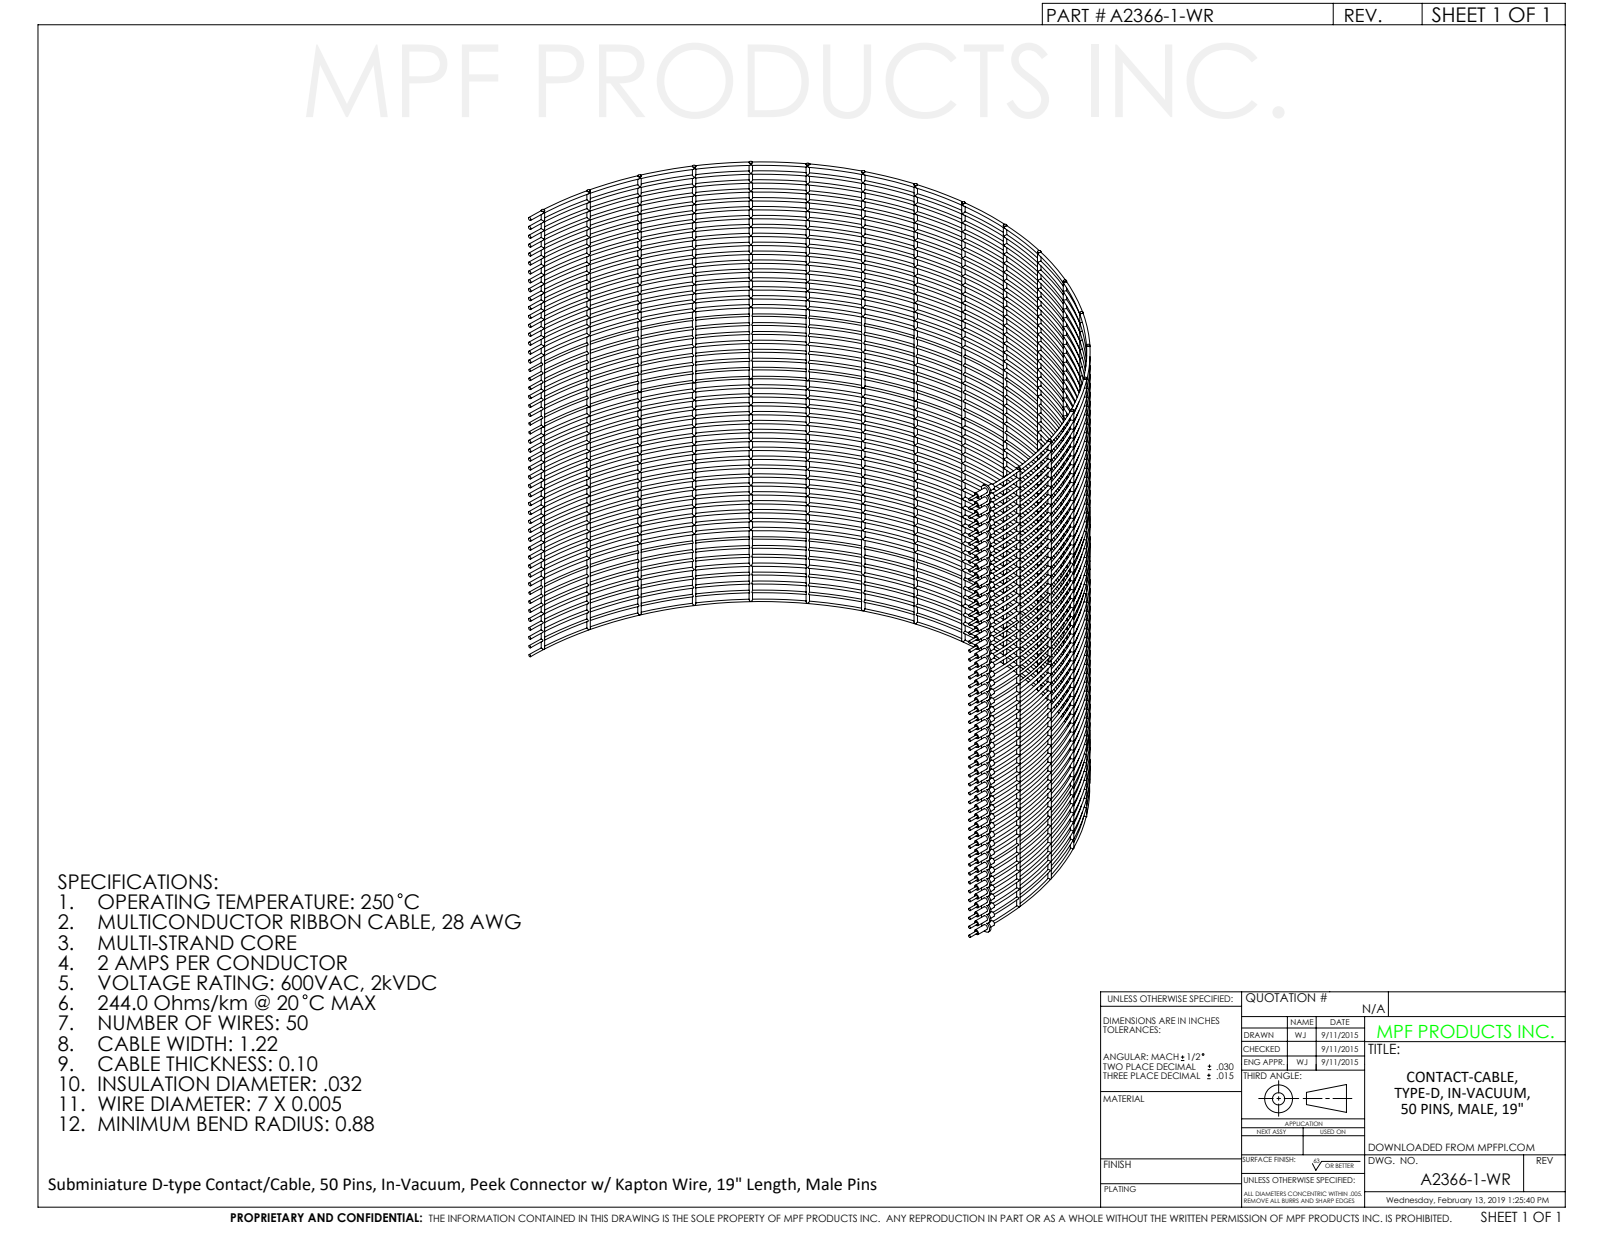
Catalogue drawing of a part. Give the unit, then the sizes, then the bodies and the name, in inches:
Units: inches
Overall size (bounding box): 6.069 × 5.005 × 3.315
Round bosses / shafts (diameter × count): ⌀0.05 ×50, ⌀0.023 ×50, ⌀0.105 ×48, ⌀0.032 ×18
Partial cylindrical surfaces — rounded edges, fillets, slot ends (radius × count): R0.053 ×2
Main face-to-face distances: 0.018, 0.074, 0.091, 0.207, 0.134, 0.116, 0.298, 0.225, 0.207, 0.091
Volume: 0.412 in³ · Surface area: 52.44 in²
Bodies: 1 solid, 3930 faces (332 planar, 1706 cylindrical, 1892 other)
Part name (STEP PRODUCT): A2366-1-WR
STEP written by: SolidWorks 2012 (CONFIG_CONTROL_DESIGN)
